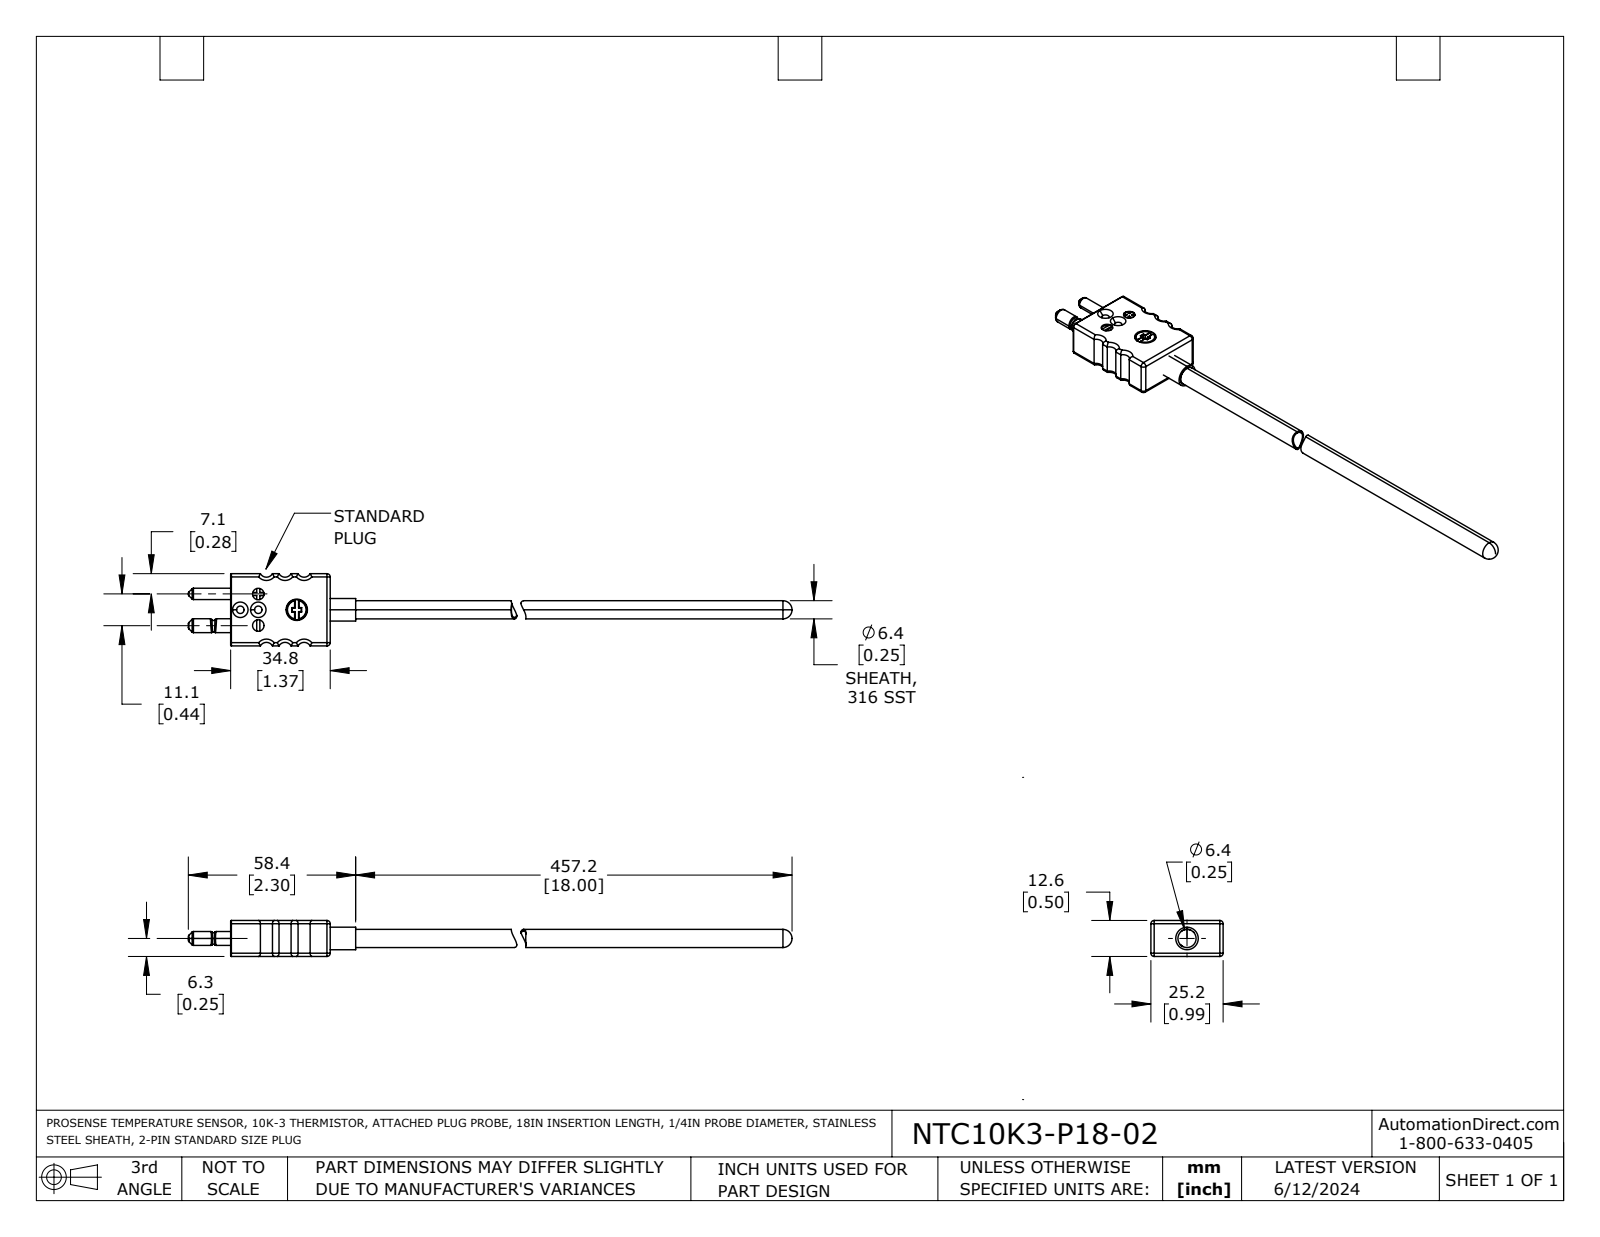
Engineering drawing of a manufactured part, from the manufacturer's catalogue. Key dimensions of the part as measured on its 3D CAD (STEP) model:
Part name (STEP PRODUCT): NTC10K3-P18-02
STEP written by: SolidWorks 2021 (AUTOMOTIVE_DESIGN)
Units: inches
Bodies: 3 solids, 201 faces (63 planar, 62 cylindrical, 76 other)
Overall size (bounding box): 20.296 × 0.993 × 0.495
Volume: 0.922 in³ · Surface area: 33.46 in²
Round holes (diameter × count): ⌀0.103 ×2, ⌀0.158 ×2, ⌀0.185 ×1, ⌀0.21 ×1, ⌀0.253 ×1, ⌀0.294 ×1, ⌀0.308 ×1
Round bosses / shafts (diameter × count): ⌀0.31 ×1, ⌀0.278 ×1, ⌀0.25 ×1, ⌀0.191 ×1, ⌀0.156 ×1, ⌀0.102 ×1
Partial cylindrical surfaces — rounded edges, fillets, slot ends (radius × count): R0.045 ×8, R0.095 ×6, R0.01 ×4
Main face-to-face distances: 0.495, 0.993, 1.369, 0.05, 0.3, 0.693, 0.394, 0.051, 0.444, 0.27
Hole centre spacings: 0.217, 0.328, 0.572, 0.247, 0.433, 0.529, 0.776
